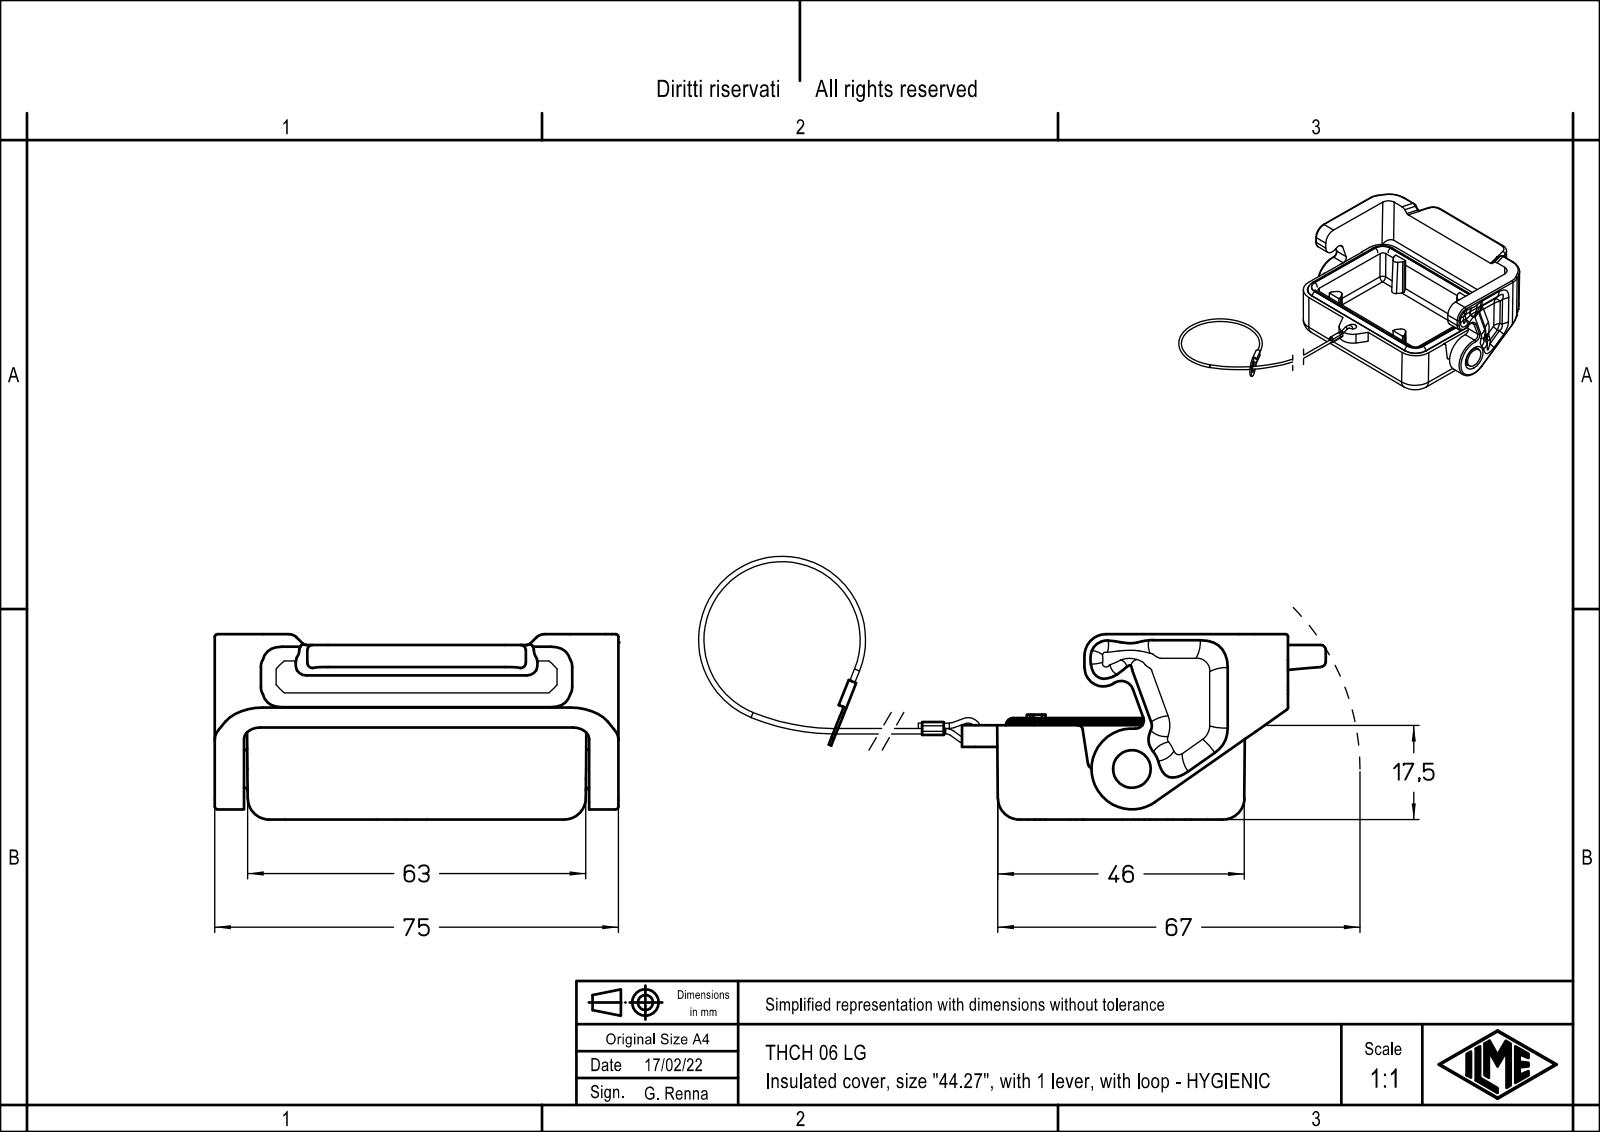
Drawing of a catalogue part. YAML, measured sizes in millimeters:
part_name: "Coperchietto_06p_leva"
step_written_by: "Creo Elements/Direct Modeling 20.1B 02-Apr-2019 (C) Parametric Technology GmbH (AUTOMOTIVE_DESIGN)"
units: millimeters
bodies: {solids: 1, faces: 407, planar: 128, cylindrical: 219, other: 60}
overall_size: [236.27, 81.38, 34.55]
volume: 42607
surface_area: 23116
round_holes:
  - {diameter: 3, count: 1}
  - {diameter: 4.2, count: 1}
round_bosses_or_shafts:
  - {diameter: 1, count: 4}
  - {diameter: 7, count: 2}
partial_cylinders:
  - {radius: 0.15, count: 44}
  - {radius: 1, count: 24}
  - {radius: 1.3, count: 16}
  - {radius: 1.5, count: 15}
  - {radius: 3, count: 9}
  - {radius: 5.5, count: 8}
  - {radius: 4, count: 7}
  - {radius: 2, count: 6}
face_to_face_distances: [5.5, 69.5, 64, 12, 17.5, 14.9, 2, 32.4, 26.9, 28.9]
